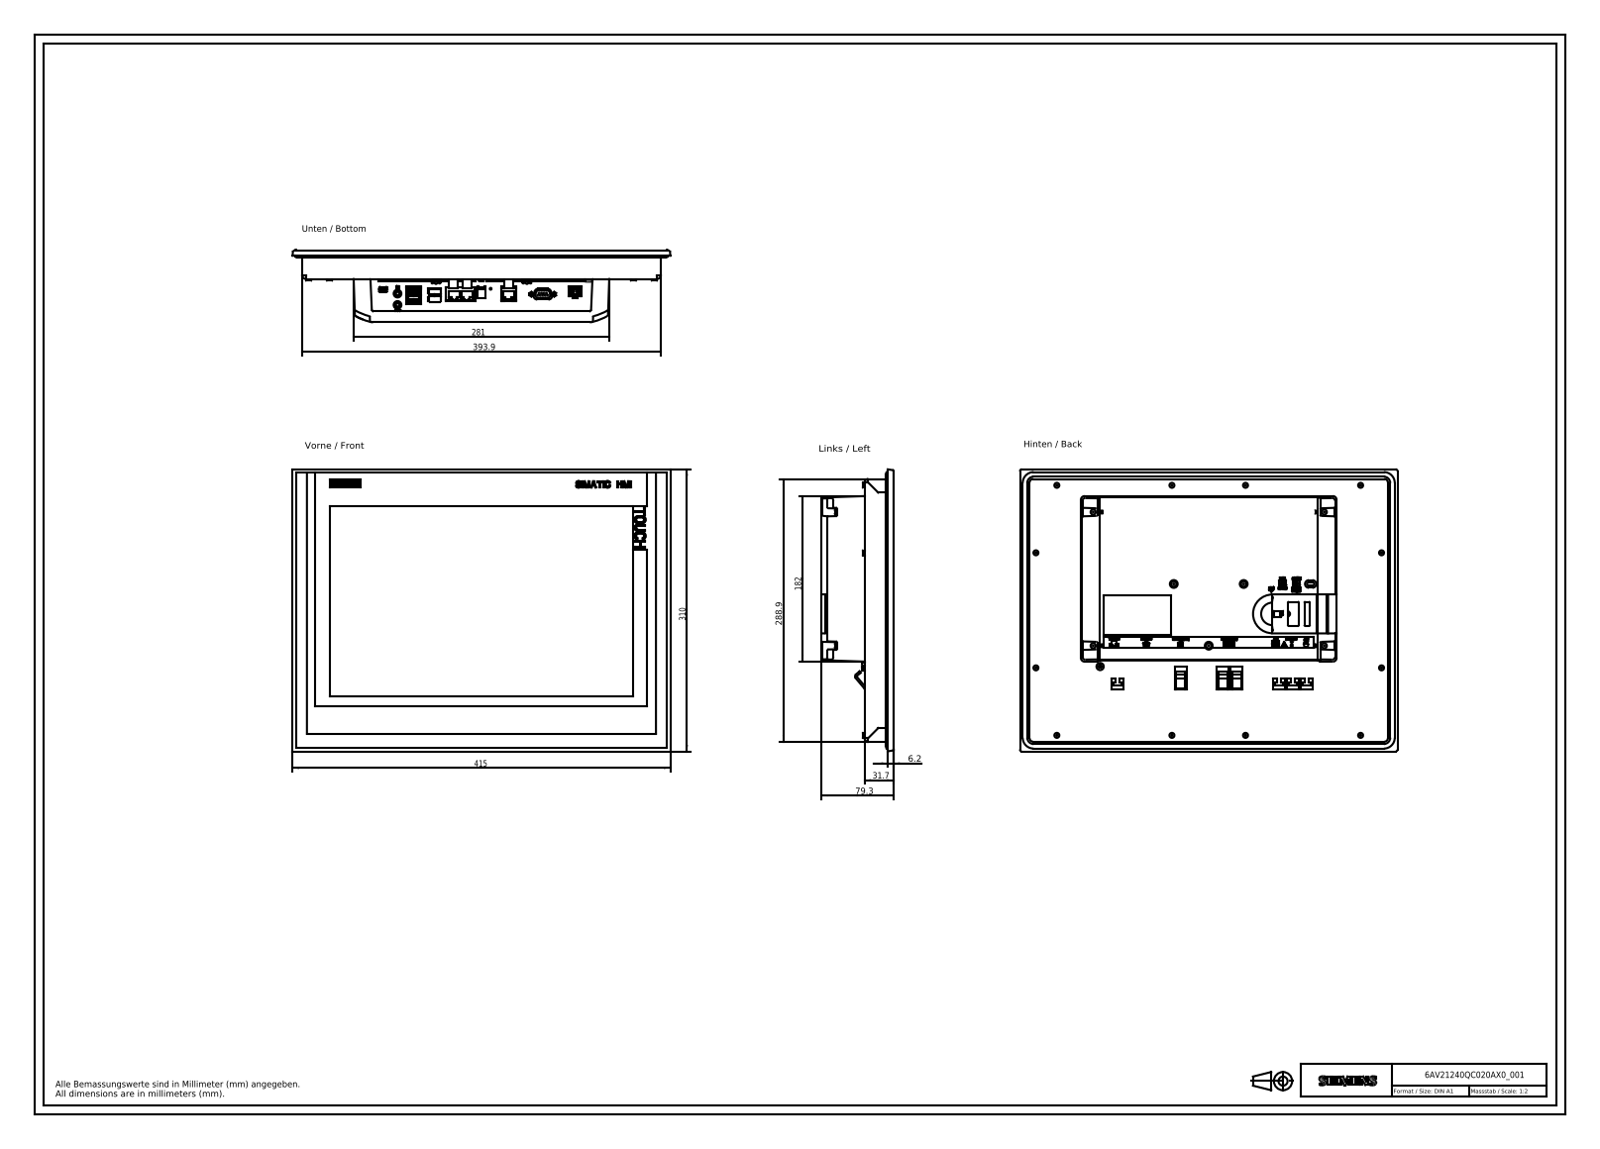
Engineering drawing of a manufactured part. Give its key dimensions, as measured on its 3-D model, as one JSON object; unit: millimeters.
{"part_name": "A5E30321192A_001; A5E30979120A_001; A5E30979119A_001; A5E30979117A_001 (+1 more)", "step_written_by": "SIEMENS PLM Software NX 7.5 (AUTOMOTIVE_DESIGN)", "units": "millimeters", "bodies": {"solids": 258, "faces": 2962, "planar": 2337, "cylindrical": 376, "other": 249}, "overall_size": [415, 310, 79.4], "volume_mm3": 5950000, "surface_area_mm2": 502130, "round_holes": [[0.8, 9], [8.02, 3], [1.81, 2], [2.4, 2], [2.84, 2], [3.8, 2], [8.5, 2]], "round_bosses_or_shafts": [[5.5, 12], [6, 8], [7, 2], [3.04, 2], [3, 2], [2.01, 2], [8, 1]], "partial_cylinders_radius": [[0.71, 72], [0.84, 48], [1.4, 12], [1.26, 8], [0.98, 4], [1.85, 4], [3.95, 4], [6.98, 4]], "face_to_face_distances": [39.1, 30.6, 9.5, 40.1, 1, 8.5, 38.1, 47.6, 78.2, 31.25], "hole_center_spacings": [2.89, 2.74, 4.83, 5.48, 7.31, 8.22, 9.92, 12.5]}
